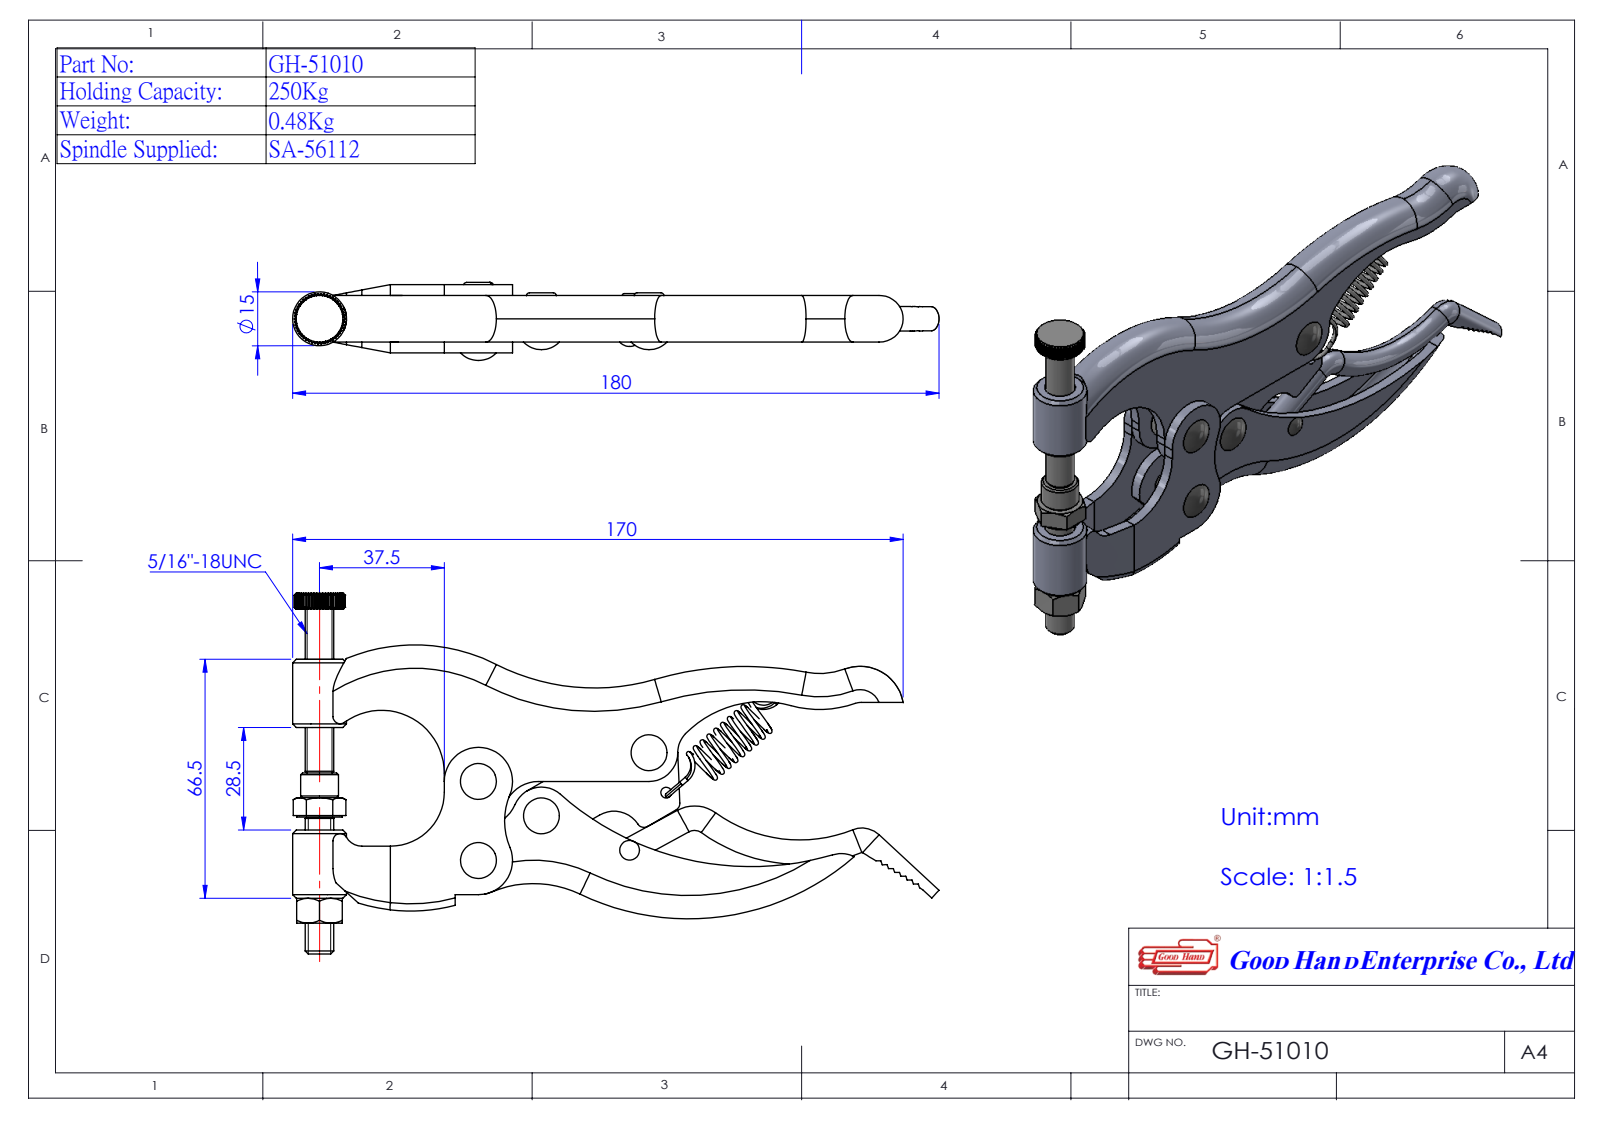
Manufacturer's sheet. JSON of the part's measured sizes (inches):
{"part_name": "GH-51010(單一); Group1^GH-51010(單一)", "step_written_by": "SolidWorks 2016 (AUTOMOTIVE_DESIGN)", "units": "inches", "bodies": {"solids": 1, "faces": 575, "planar": 201, "cylindrical": 159, "other": 215}, "overall_size": [7.087, 3.951, 0.856], "volume_in3": 3.844, "surface_area_in2": 61.4, "round_bosses_or_shafts": [[0.268, 2], [0.248, 2], [0.197, 2], [0.748, 1], [0.591, 1], [0.5, 1], [0.413, 1], [0.313, 1]], "partial_cylinders_radius": [[0.079, 4], [0.315, 3], [0.394, 3], [0.197, 2], [0.276, 2], [1.181, 2], [0.024, 1], [0.295, 1]], "face_to_face_distances": [0.118, 0.394, 0.512, 0.276, 0.256, 0.236, 0.63, 0.138, 0.374, 0.02]}
